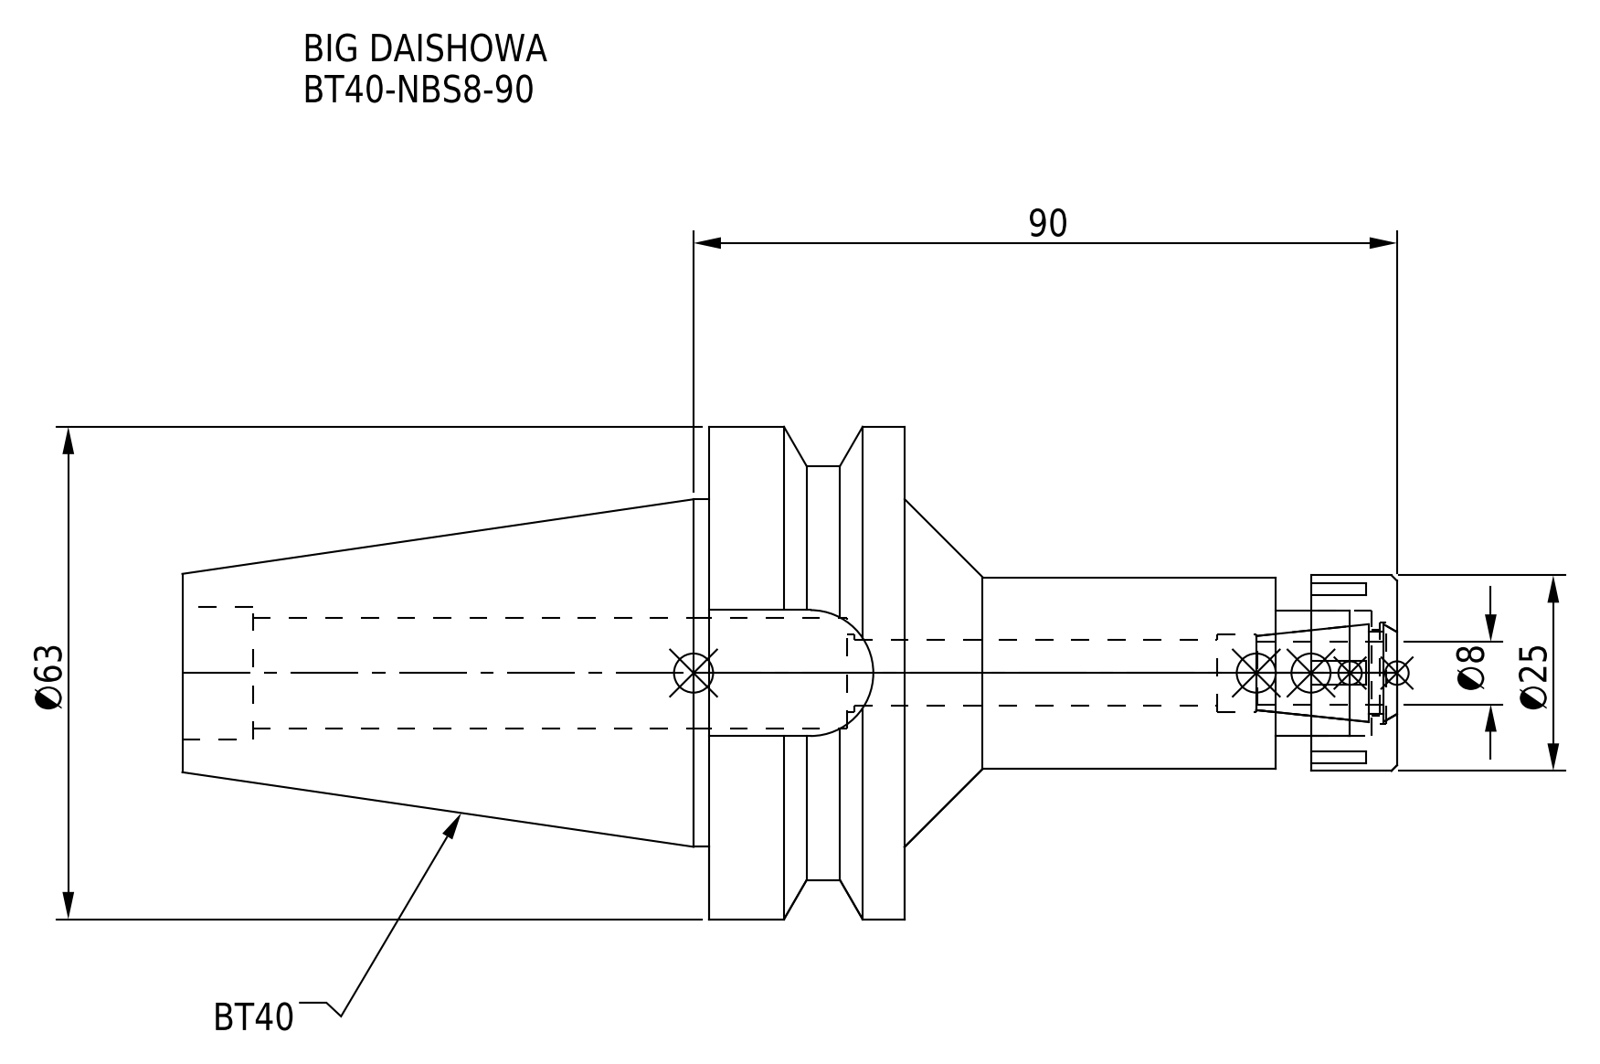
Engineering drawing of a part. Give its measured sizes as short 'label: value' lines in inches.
name: BT40NB08090-080_ASM.stp; NBN8_1.stp; DXF_TEMP_ASSY_ASM_4_ASM.stp; BT40-NBS8-90_1.stp (+3 more)
written by: SolidWorks 2019 (CONFIG_CONTROL_DESIGN)
unit: in
bodies: 2 solids, 93 faces (45 planar, 34 cylindrical, 14 other)
size: 6.118 × 2.48 × 2.48
volume: 9.066 in³; area: 47.14 in²
holes: 1× ⌀0.331, 1× ⌀0.394, 1× ⌀0.433, 1× ⌀0.512, 1× ⌀0.559, 1× ⌀0.63, 1× ⌀0.669
bosses: 1× ⌀2.48, 1× ⌀2.087, 1× ⌀1.75, 1× ⌀0.984, 1× ⌀0.965
rounds: 1× R0.317
face distances: 0.984, 2.48, 3.465, 1.772, 3.031, 6.118, 3.638, 2.654, 0.61, 1.87
